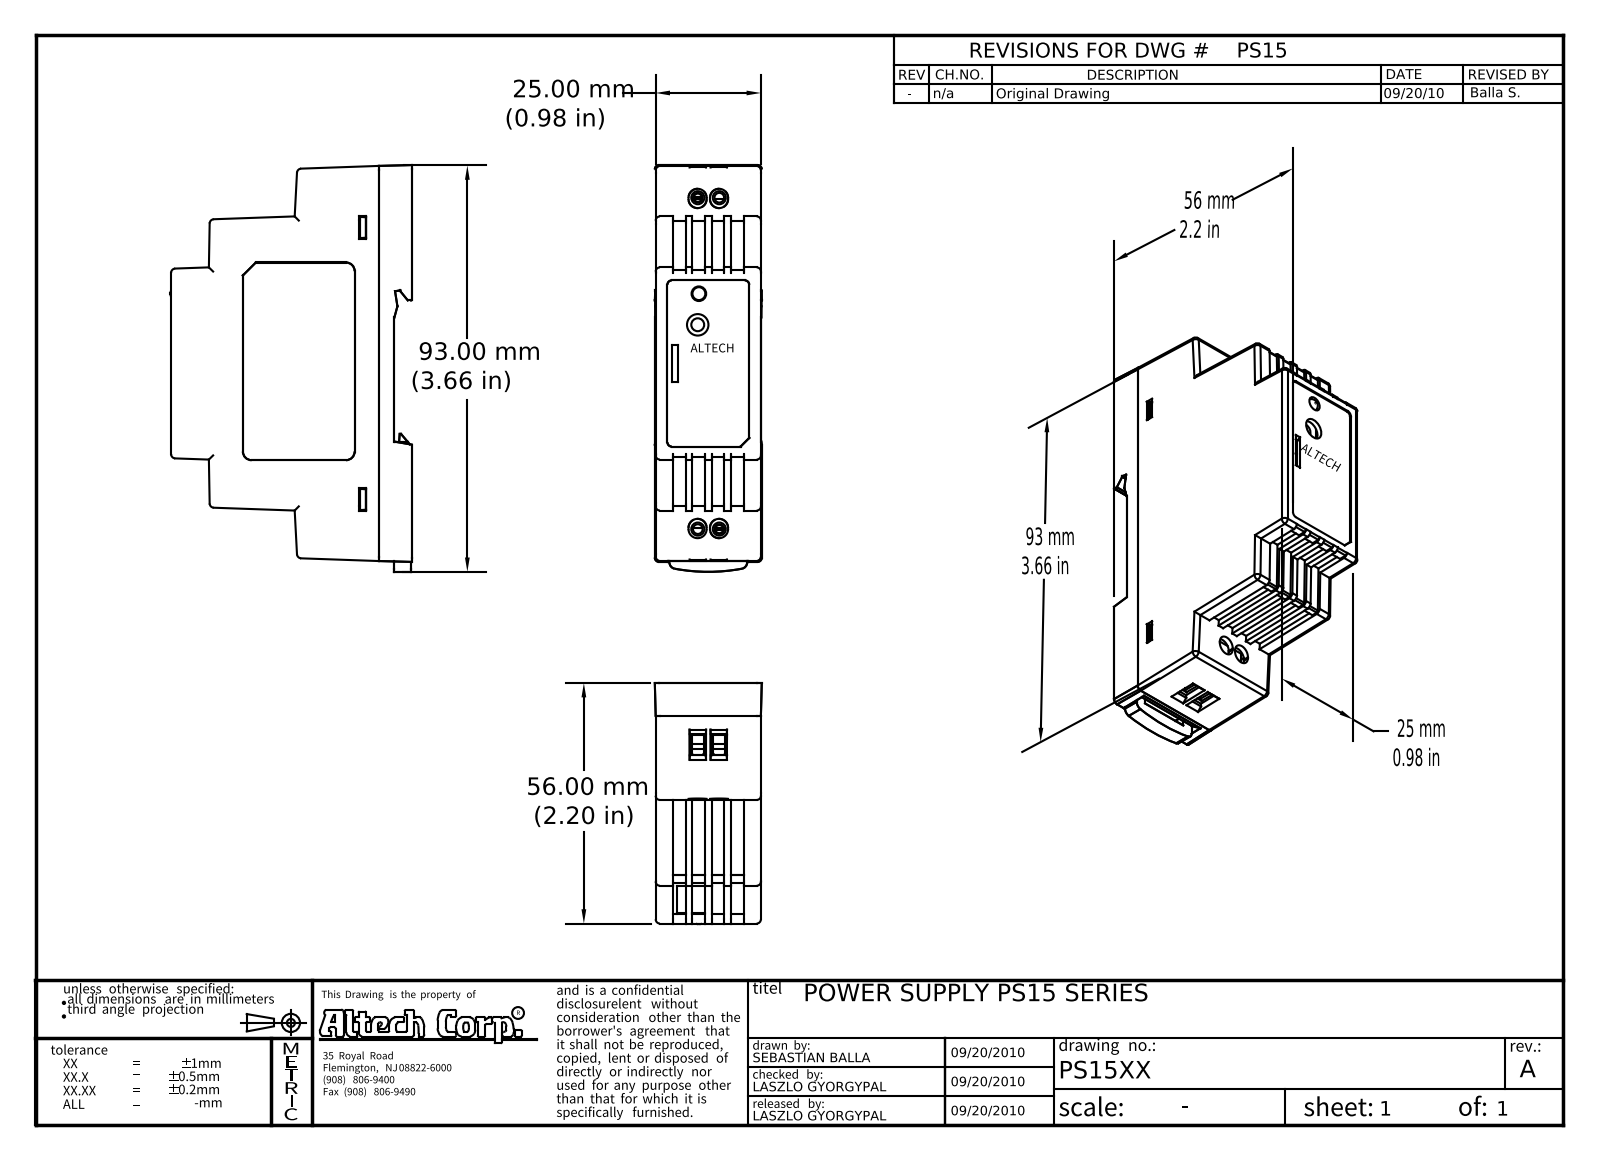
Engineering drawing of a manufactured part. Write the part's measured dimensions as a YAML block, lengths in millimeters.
part_name: "PS15; ALL-INNER-PARTS; 3P-CONECT.1; LED (+3 more)"
step_written_by: "Autodesk Inventor 2009 (AUTOMOTIVE_DESIGN)"
units: millimeters
bodies: {solids: 5, faces: 1112, planar: 878, cylindrical: 170, other: 64}
overall_size: [94.73, 56.19, 25.01]
volume: 11520
surface_area: 42506
round_holes:
  - {diameter: 2.25, count: 4}
  - {diameter: 3, count: 1}
  - {diameter: 3.4, count: 1}
  - {diameter: 5, count: 1}
round_bosses_or_shafts:
  - {diameter: 1.9, count: 2}
  - {diameter: 1.4, count: 2}
  - {diameter: 1.3, count: 2}
  - {diameter: 3, count: 1}
partial_cylinders:
  - {radius: 1, count: 36}
  - {radius: 0.2, count: 26}
  - {radius: 0.5, count: 20}
  - {radius: 0.3, count: 12}
  - {radius: 0.4, count: 6}
  - {radius: 1.5, count: 4}
  - {radius: 13.96, count: 4}
  - {radius: 20.18, count: 4}
face_to_face_distances: [24.5, 2.5, 2.45, 24.4, 2.4, 4, 4.05, 4.1, 6.5, 2.55]
hole_center_spacings: [5, 77.16, 77.32, 0.81, 7.25, 7.32, 22.34, 22.86]
